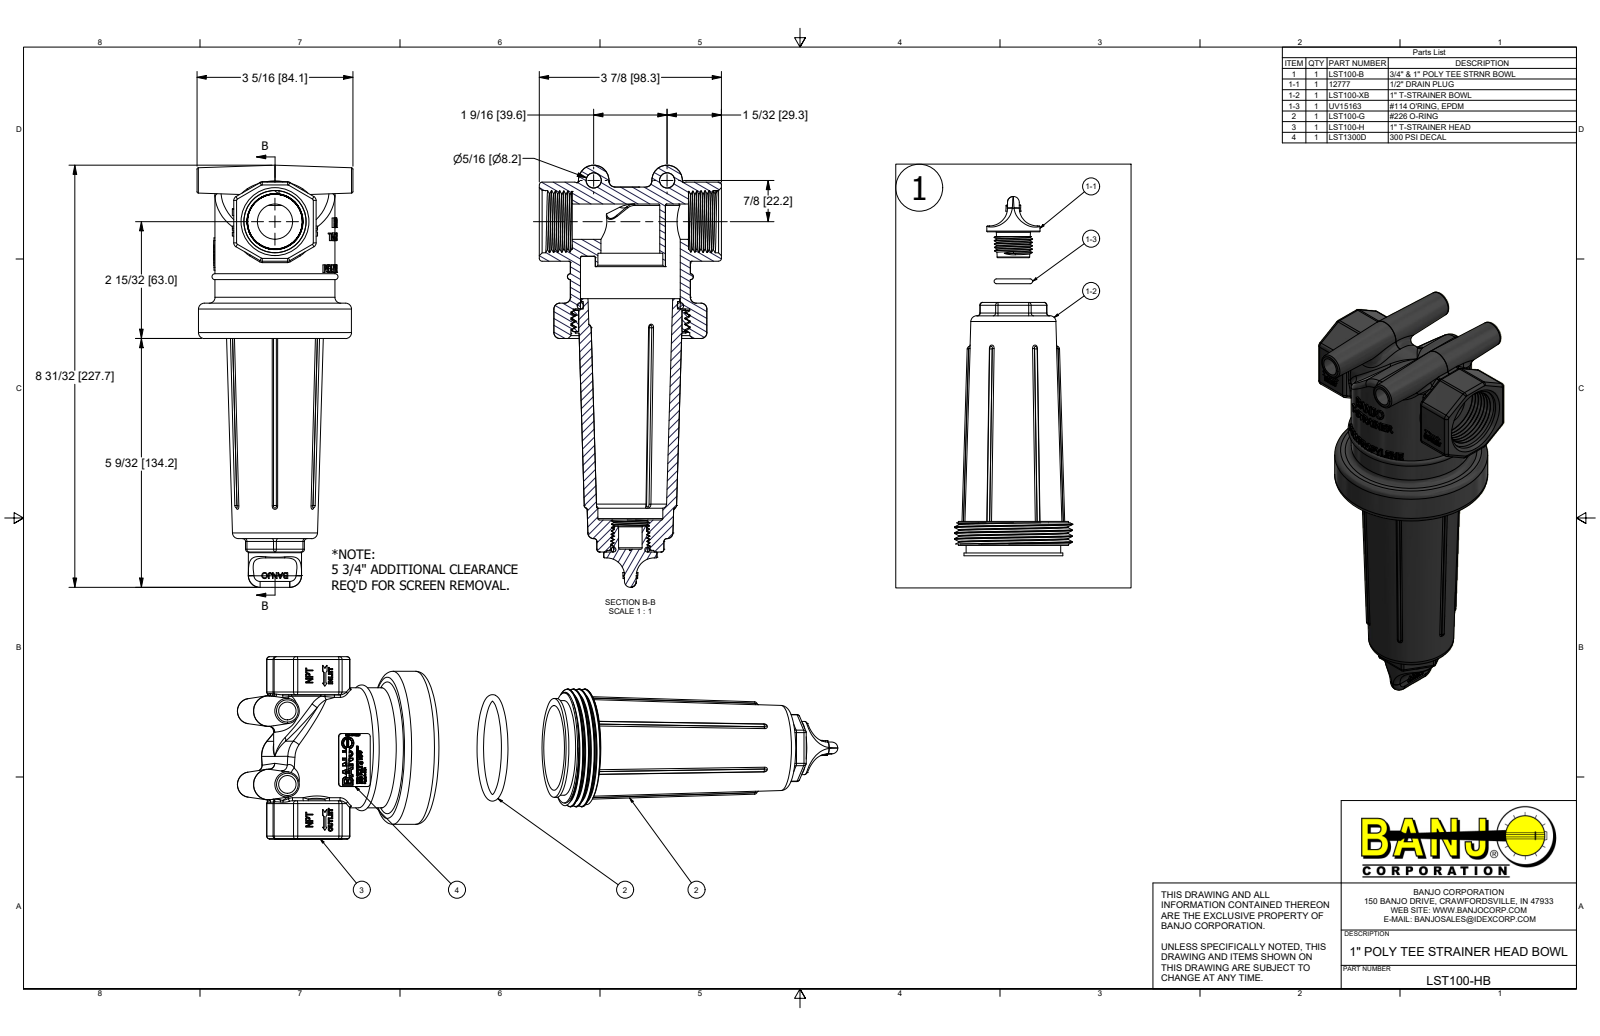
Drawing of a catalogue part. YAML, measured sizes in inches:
part_name: "LST100-HB; CE050D; LST100-B; LST100-XB (+5 more)"
step_written_by: "Autodesk Inventor 2019 (AUTOMOTIVE_DESIGN)"
units: inches
bodies: {solids: 8, faces: 2520, planar: 1371, cylindrical: 226, other: 923}
overall_size: [38.886, 14.249, 3.313]
volume: 17.9
surface_area: 429.8
round_holes:
  - {diameter: 0.181, count: 1}
  - {diameter: 0.257, count: 1}
  - {diameter: 0.5, count: 1}
  - {diameter: 0.75, count: 1}
  - {diameter: 1.005, count: 1}
  - {diameter: 1.25, count: 1}
  - {diameter: 1.38, count: 1}
  - {diameter: 2.12, count: 1}
  - {diameter: 2.195, count: 1}
  - {diameter: 2.396, count: 1}
  - {diameter: 2.525, count: 1}
round_bosses_or_shafts:
  - {diameter: 3.25, count: 1}
  - {diameter: 2.55, count: 1}
  - {diameter: 2.5, count: 1}
  - {diameter: 2.34, count: 1}
  - {diameter: 2.1, count: 1}
  - {diameter: 2.01, count: 1}
  - {diameter: 1.49, count: 1}
  - {diameter: 1.47, count: 1}
partial_cylinders:
  - {radius: 0.06, count: 52}
  - {radius: 0.03, count: 11}
  - {radius: 0.094, count: 8}
  - {radius: 0.026, count: 2}
  - {radius: 0.033, count: 2}
  - {radius: 0.035, count: 2}
  - {radius: 0.063, count: 2}
  - {radius: 0.07, count: 2}
face_to_face_distances: [1.75, 0.03, 0.48, 0.7, 0.625, 0.595, 0.25, 0.145, 0.45, 3.17]
